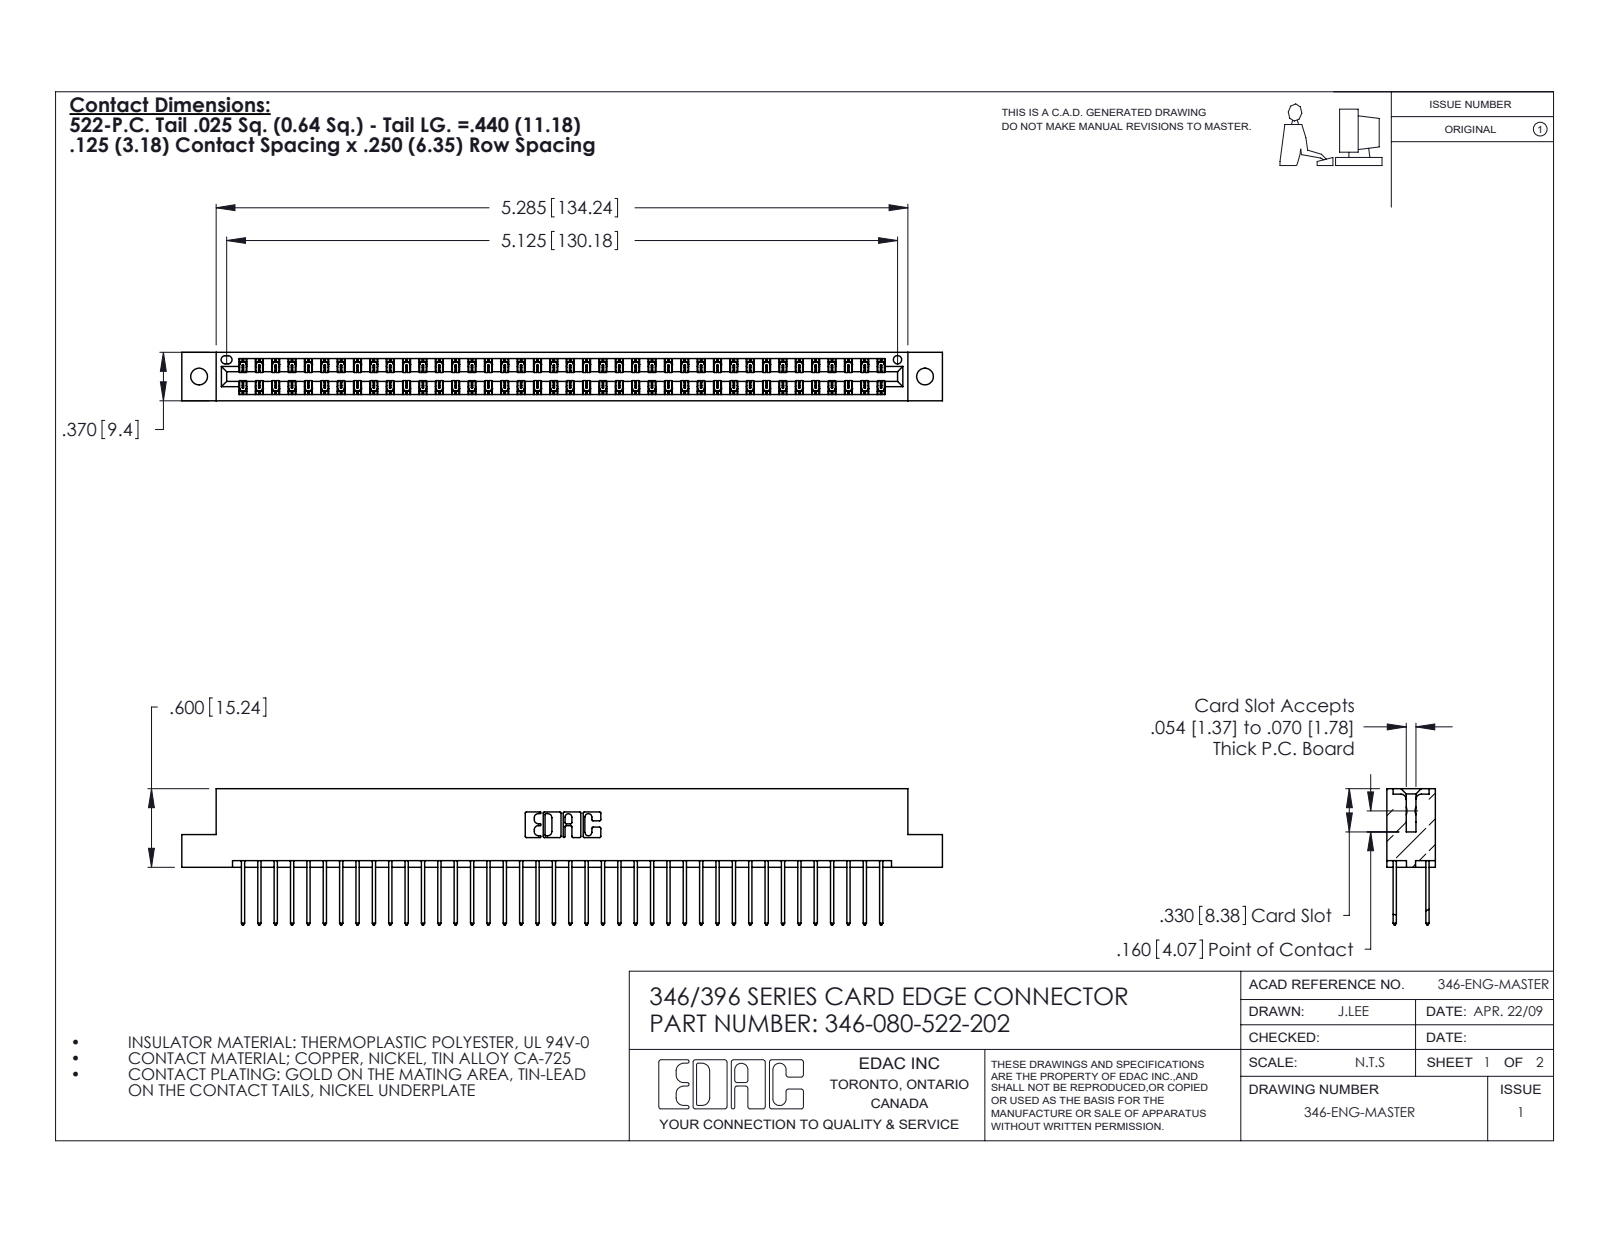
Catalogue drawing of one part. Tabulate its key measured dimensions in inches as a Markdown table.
| quantity | value |
| --- | --- |
| part name | 346-080-522-202; 346 Part_Flush Mounting Lugs - 0.128 Dia; 345-292-001_345-293-122 |
| STEP written by | SolidWorks 2020 (CONFIG_CONTROL_DESIGN) |
| units | inches |
| bodies | 81 solids, 4282 faces (2876 planar, 1406 cylindrical, 0 other) |
| overall size | 5.81 × 1.04 × 0.37 |
| volume | 0.887 in³ |
| surface area | 31.99 in² |
| round holes (diameter × count) | 0.128 × 2, 0.064 × 1 |
| partial cylindrical surfaces (radius × count) | 0.006 × 120, 0.01 × 80, 0.01 × 22, 0.007 × 6, 0.031 × 6, 0.026 × 3, 0.014 × 2, 0.022 × 2 |
| main face-to-face distances | 0.048, 0.322, 0.25, 0.37, 0.072, 0.298, 0.025, 0.275, 0.148, 0.222 |
| hole center spacings | 0.246, 5.336, 5.545 |
